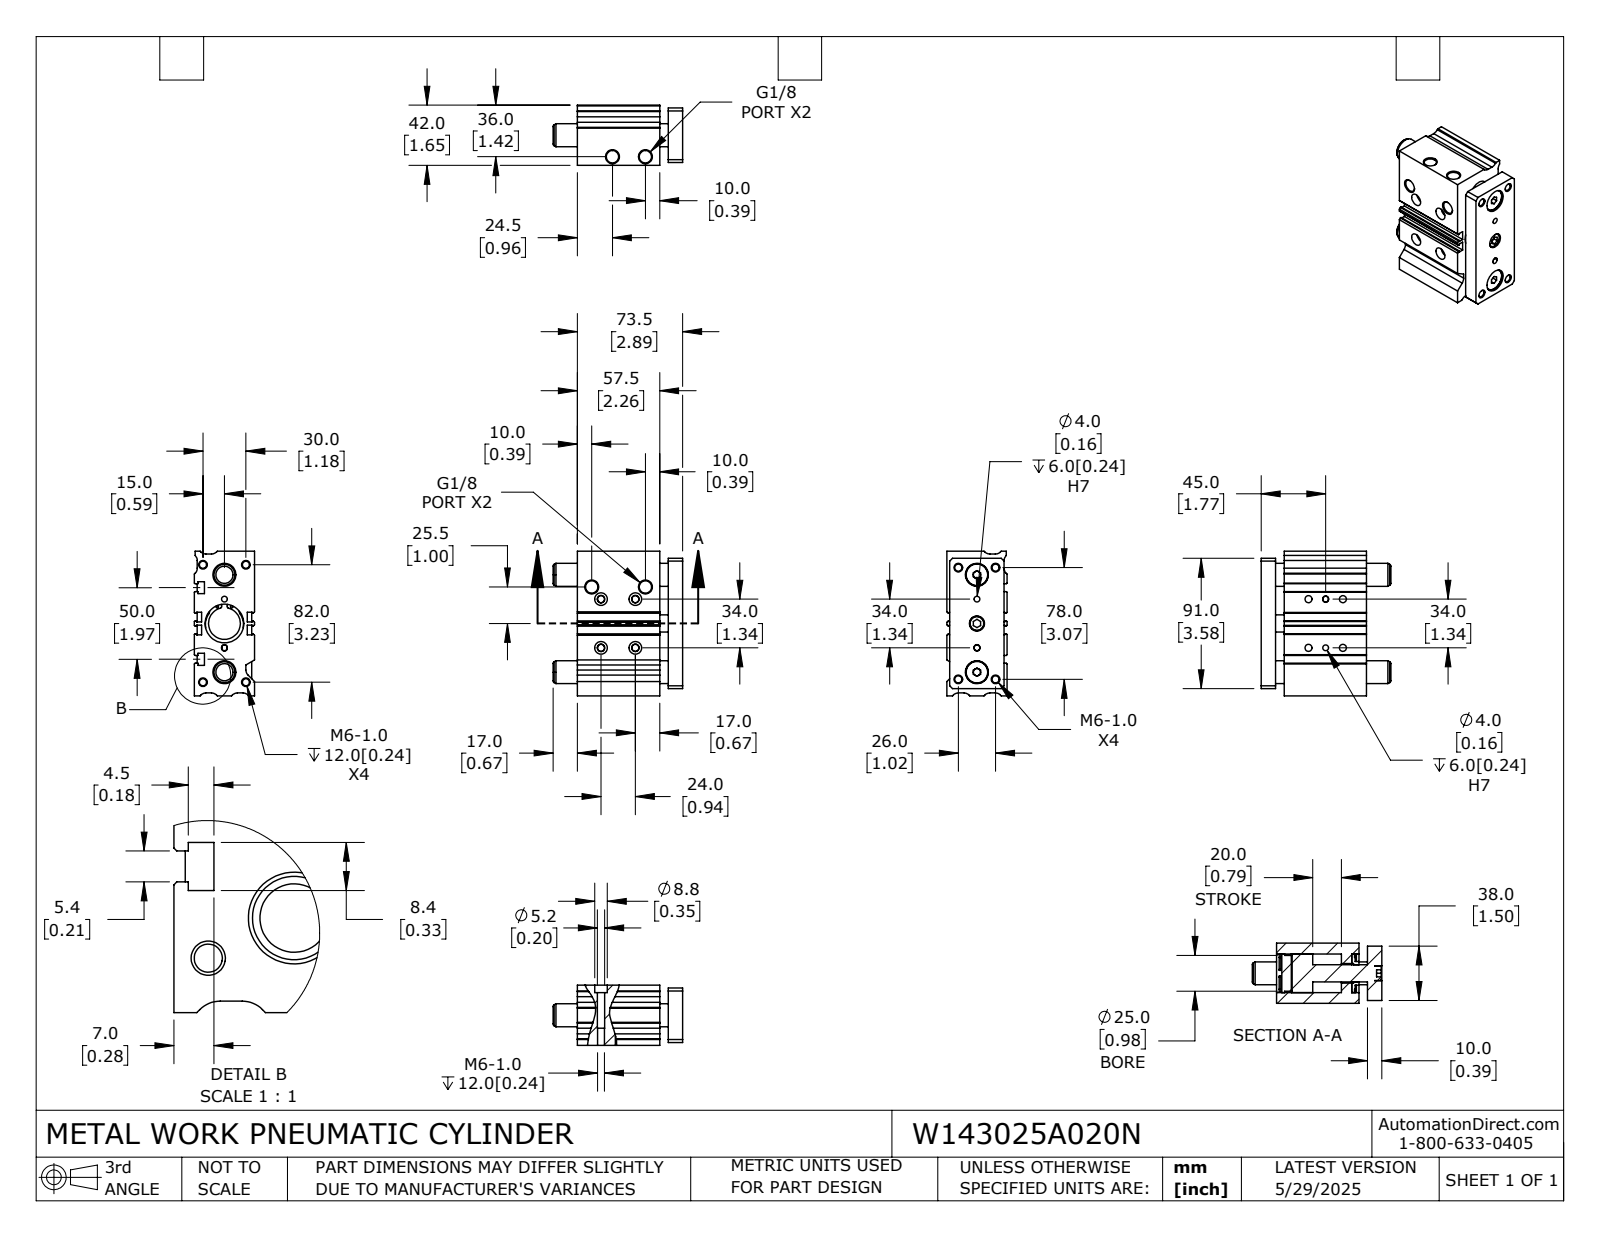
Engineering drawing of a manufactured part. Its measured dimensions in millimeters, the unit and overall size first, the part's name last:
Units: millimetres
Overall size (bounding box): 101 × 90.5 × 42
Round holes (diameter × count): ⌀4.9 ×8, ⌀1.7 ×4, ⌀4 ×4, ⌀4.9 ×4, ⌀5.2 ×4, ⌀8.6 ×4, ⌀8.8 ×4, ⌀16 ×2, ⌀10.5 ×1, ⌀12 ×1, ⌀13.7 ×1, ⌀22.2 ×1
Round bosses / shafts (diameter × count): ⌀15.5 ×2, ⌀27 ×1, ⌀25 ×1, ⌀16.5 ×1, ⌀10 ×1
Partial cylindrical surfaces — rounded edges, fillets, slot ends (radius × count): R1 ×12, R5 ×9, R2 ×8, R13.3 ×2, R14.2 ×1
Main face-to-face distances: 5, 2, 42, 6, 35, 16, 10, 73.5, 63.5, 57.5
Hole centre spacings: 34, 2.8, 7.4, 12, 12.7, 13.9, 16.6, 17
Volume: 245 600 mm³ · Surface area: 70 970 mm²
Bodies: 6 solids, 390 faces (191 planar, 157 cylindrical, 42 other)
Part name (STEP PRODUCT): W143025A020N; W143025A020N_BODY; W143025A020N_ROD
STEP written by: SolidWorks 2024 (CONFIG_CONTROL_DESIGN)
